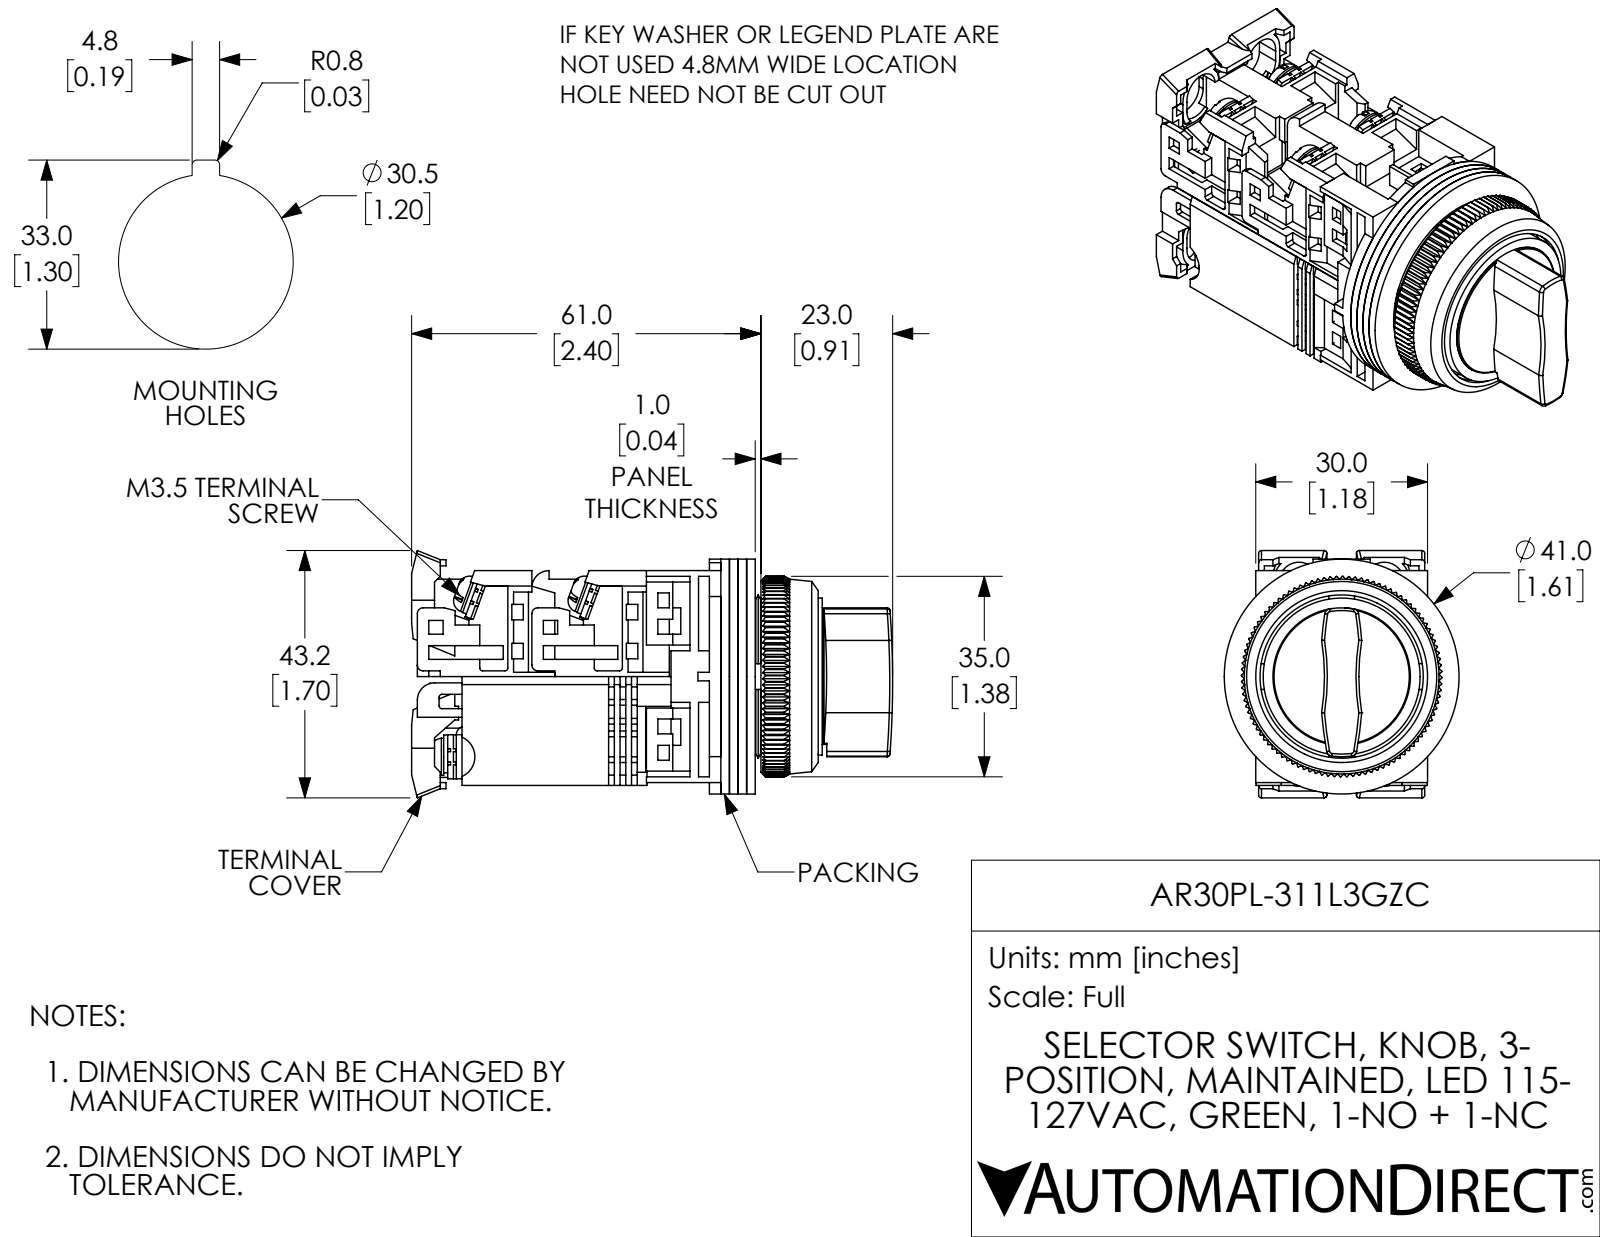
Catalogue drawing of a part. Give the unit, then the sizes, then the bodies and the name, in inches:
Units: inches
Overall size (bounding box): 3.307 × 1.7 × 1.614
Round holes (diameter × count): ⌀0.138 ×8, ⌀0.142 ×6, ⌀0.118 ×3, ⌀0.472 ×1, ⌀0.709 ×1, ⌀0.768 ×1, ⌀0.827 ×1, ⌀1.122 ×1, ⌀1.181 ×1, ⌀1.252 ×1
Round bosses / shafts (diameter × count): ⌀0.26 ×6, ⌀0.138 ×4, ⌀0.063 ×2, ⌀1.614 ×1, ⌀1.15 ×1, ⌀1.079 ×1, ⌀0.945 ×1, ⌀0.886 ×1
Partial cylindrical surfaces — rounded edges, fillets, slot ends (radius × count): R0.059 ×25, R0.02 ×15, R0.039 ×8, R0.138 ×4, R0.177 ×4, R0.118 ×3, R1.575 ×2, R2.953 ×2
Main face-to-face distances: 0.059, 0.118, 0.177, 0.039, 0.748, 0.079, 0.787, 0.063, 0.689, 0.197
Hole centre spacings: 0.579, 0.269, 0.638, 0.297, 0.624, 0.02, 0.302, 0.583
Volume: 3.442 in³ · Surface area: 70.72 in²
Bodies: 34 solids, 2724 faces (2033 planar, 354 cylindrical, 337 other)
Part name (STEP PRODUCT): AR30PL-311L3GZC
STEP written by: SolidWorks 2017 (AUTOMOTIVE_DESIGN)
